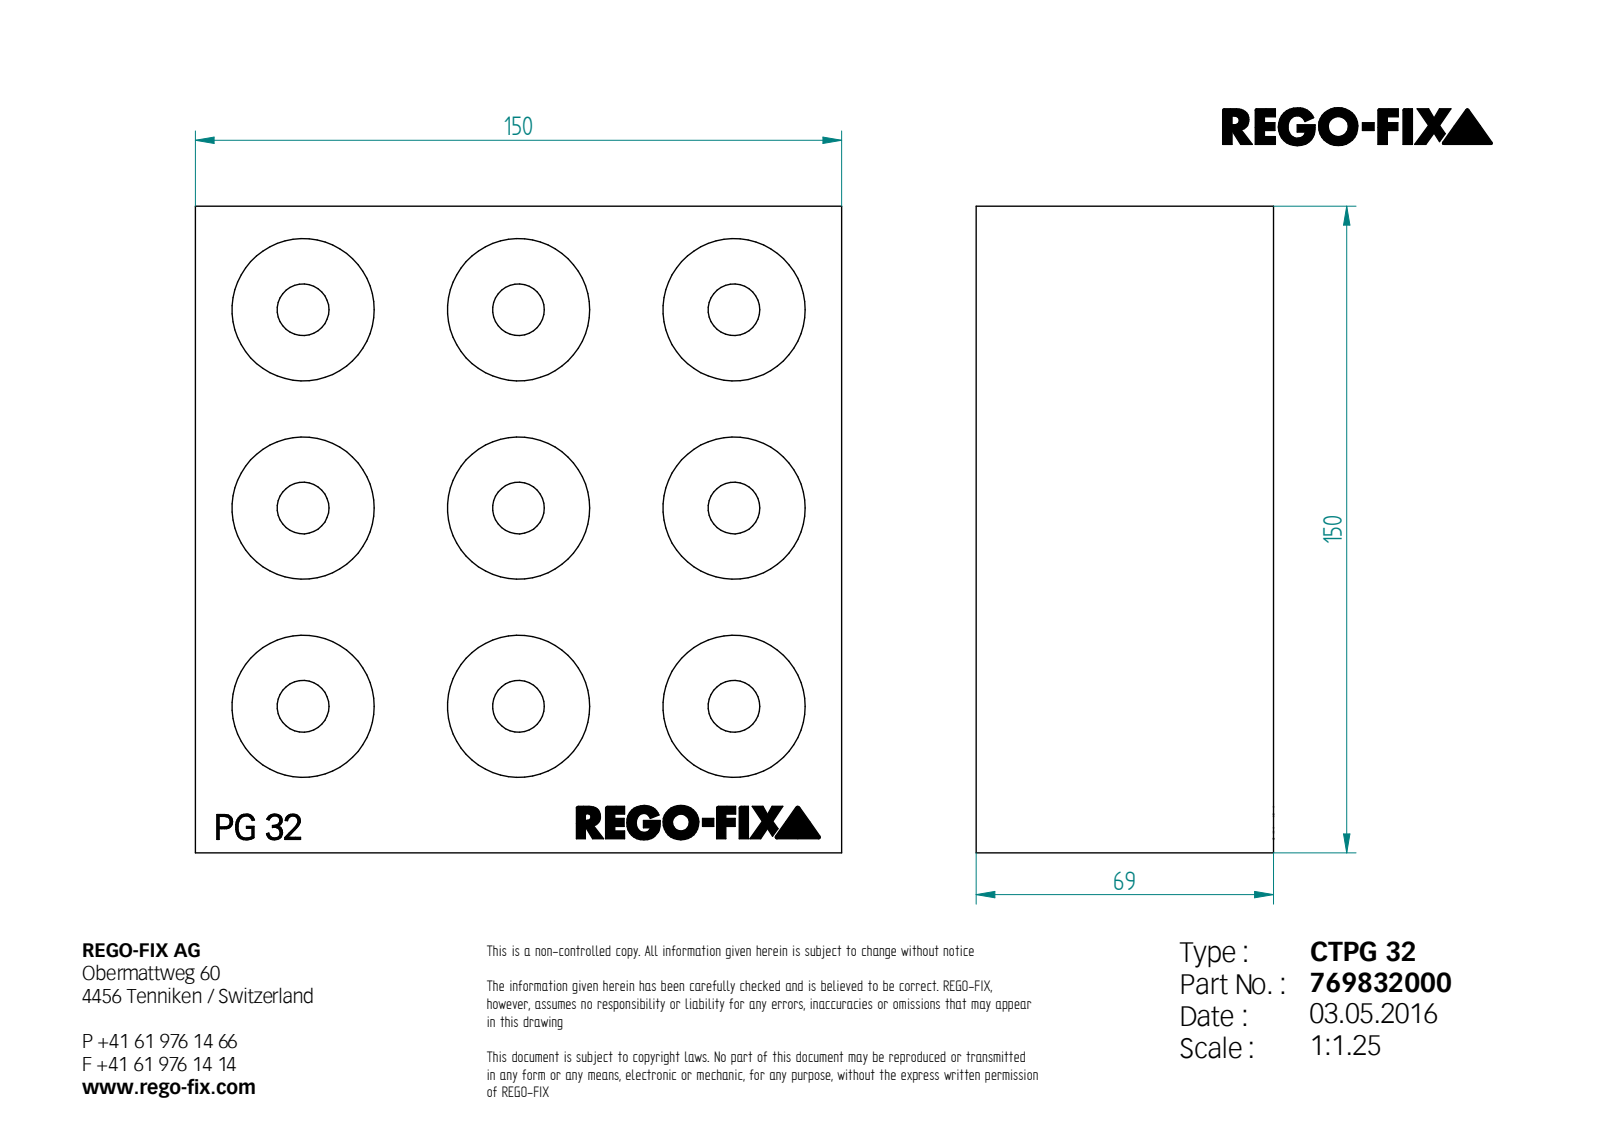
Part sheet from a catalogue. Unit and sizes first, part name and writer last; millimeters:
Units: millimetres
Overall size (bounding box): 150 × 150 × 69
Round holes (diameter × count): ⌀12 ×9, ⌀33 ×9
Main face-to-face distances: 150, 69, 59.5, 9.5, 5.5, 63.5, 4, 59.4, 63.4, 68.9
Hole centre spacings: 67.94, 46, 50, 104.71, 110.07, 92, 100, 135.88
Volume: 1 090 000 mm³ · Surface area: 143 325 mm²
Bodies: 1 solid, 149 faces (107 planar, 18 cylindrical, 24 other)
STEP written by: Unknown (AUTOMOTIVE_DESIGN)
